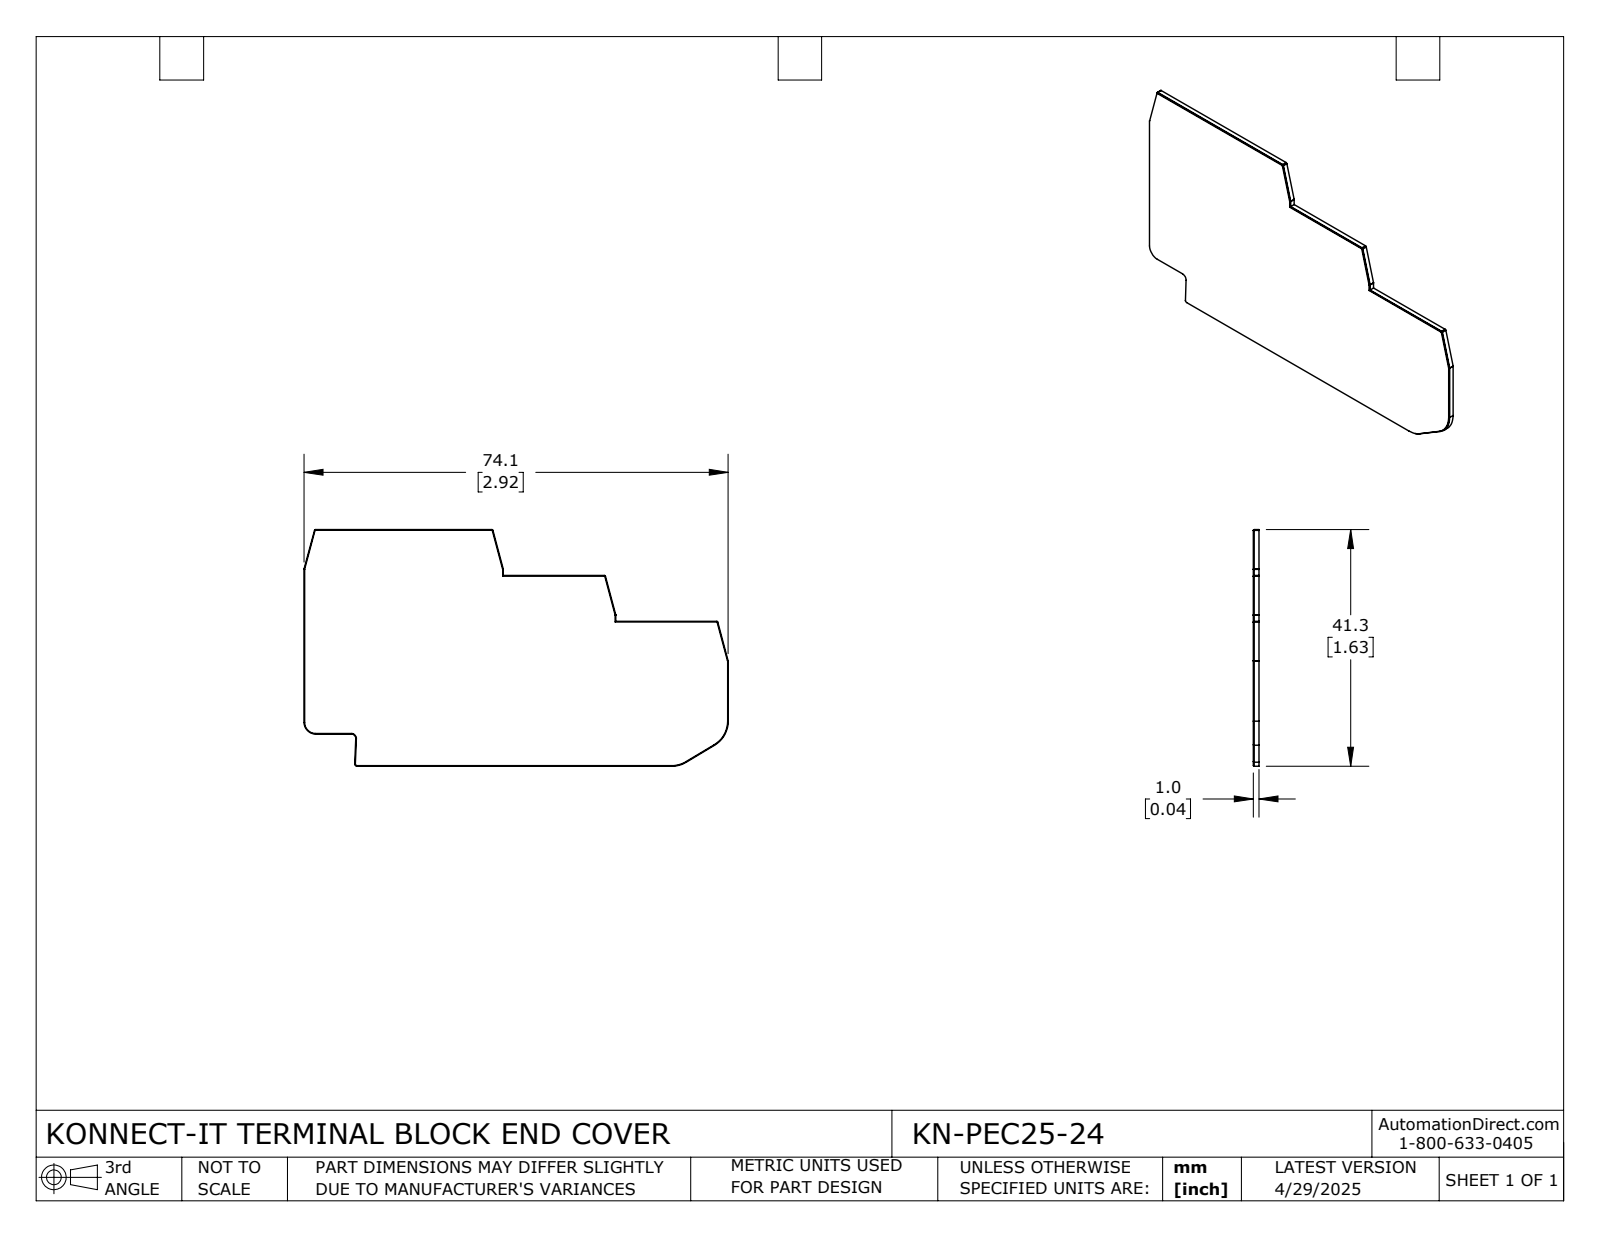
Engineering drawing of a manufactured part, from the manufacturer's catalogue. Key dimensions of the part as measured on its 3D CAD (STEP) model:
Part name (STEP PRODUCT): KN-PEC25-24
STEP written by: SolidWorks 2024 (CONFIG_CONTROL_DESIGN)
Units: millimetres
Bodies: 1 solid, 62 faces (35 planar, 27 cylindrical, 0 other)
Overall size (bounding box): 74.05 × 41.3 × 1
Volume: 2 485 mm³ · Surface area: 5 194 mm²
Partial cylindrical surfaces — rounded edges, fillets, slot ends (radius × count): R0.1 ×8, R0.2 ×8, R4.9 ×2, R0.3 ×1, R0.4 ×1, R0.78 ×1, R0.88 ×1, R1.9 ×1
Main face-to-face distances: 1, 41.31, 0.85, 16.01, 8, 8.01, 25.3, 33.3, 41.21, 25.2
